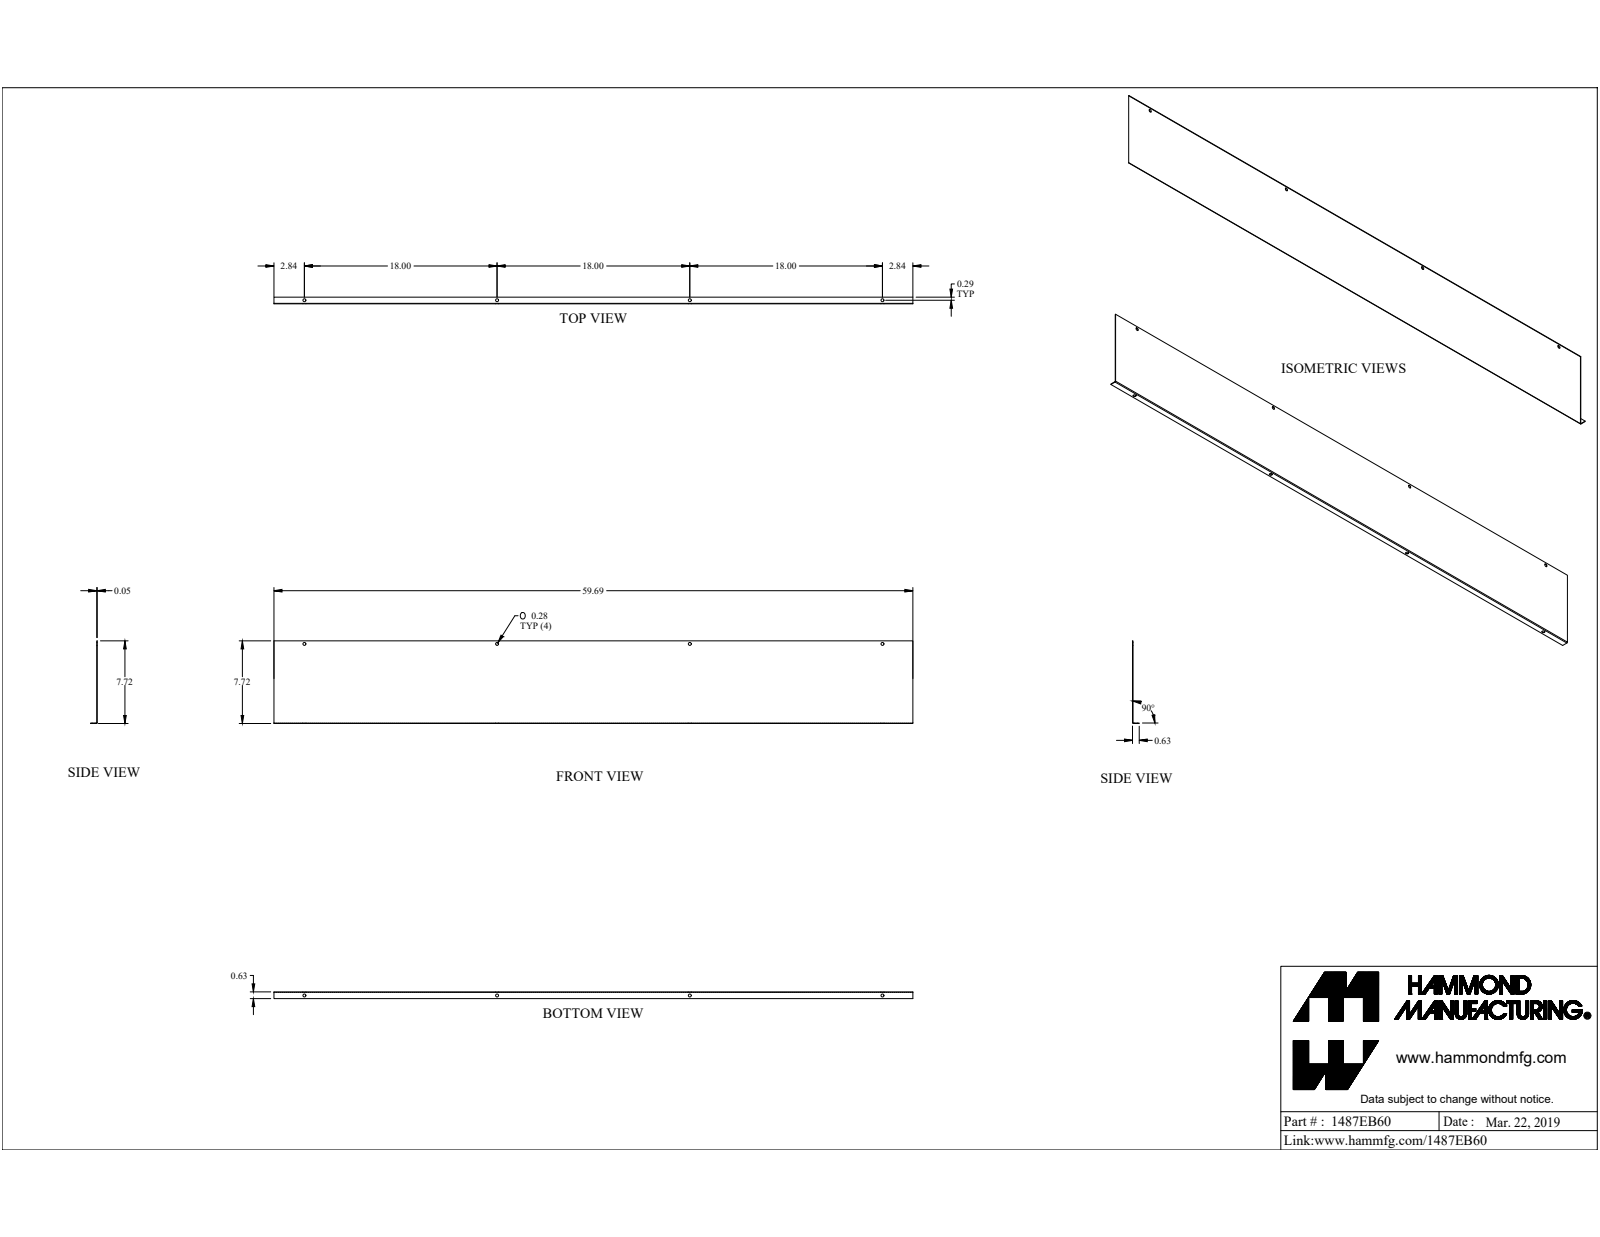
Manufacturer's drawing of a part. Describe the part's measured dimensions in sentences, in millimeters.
The part is named "1487EB60". Its 3-D file was written by "SolidWorks 2019 (CONFIG_CONTROL_DESIGN)". It is 4 solids with 63 faces: 33 planar, 15 cylindrical and 15 other. Overall it measures 1516 by 208.7 by 21.4 millimeters. Its volume is 389 200 cubic millimeters and its surface area 642 300 square millimeters. Round holes: 8 of diameter 7.1, 1 of diameter 6.4, 1 of diameter 6.6. Round bosses or shafts: 1 of diameter 13, 1 of diameter 11.1, 1 of diameter 5.7. Partial cylindrical surfaces (rounded edges, fillets, slot ends): 1 of radius 0.6, 1 of radius 1.8. The main face-to-face distances are 1.2, 15.9, 14.7, 196, 194.8, 1516, 0.8, 0.5, 15.1, 11.1. The hole center spacings are 457.2, 914.4, 228.8, 685.9, 1371.6, 296.4, 296.4, 711.3.
